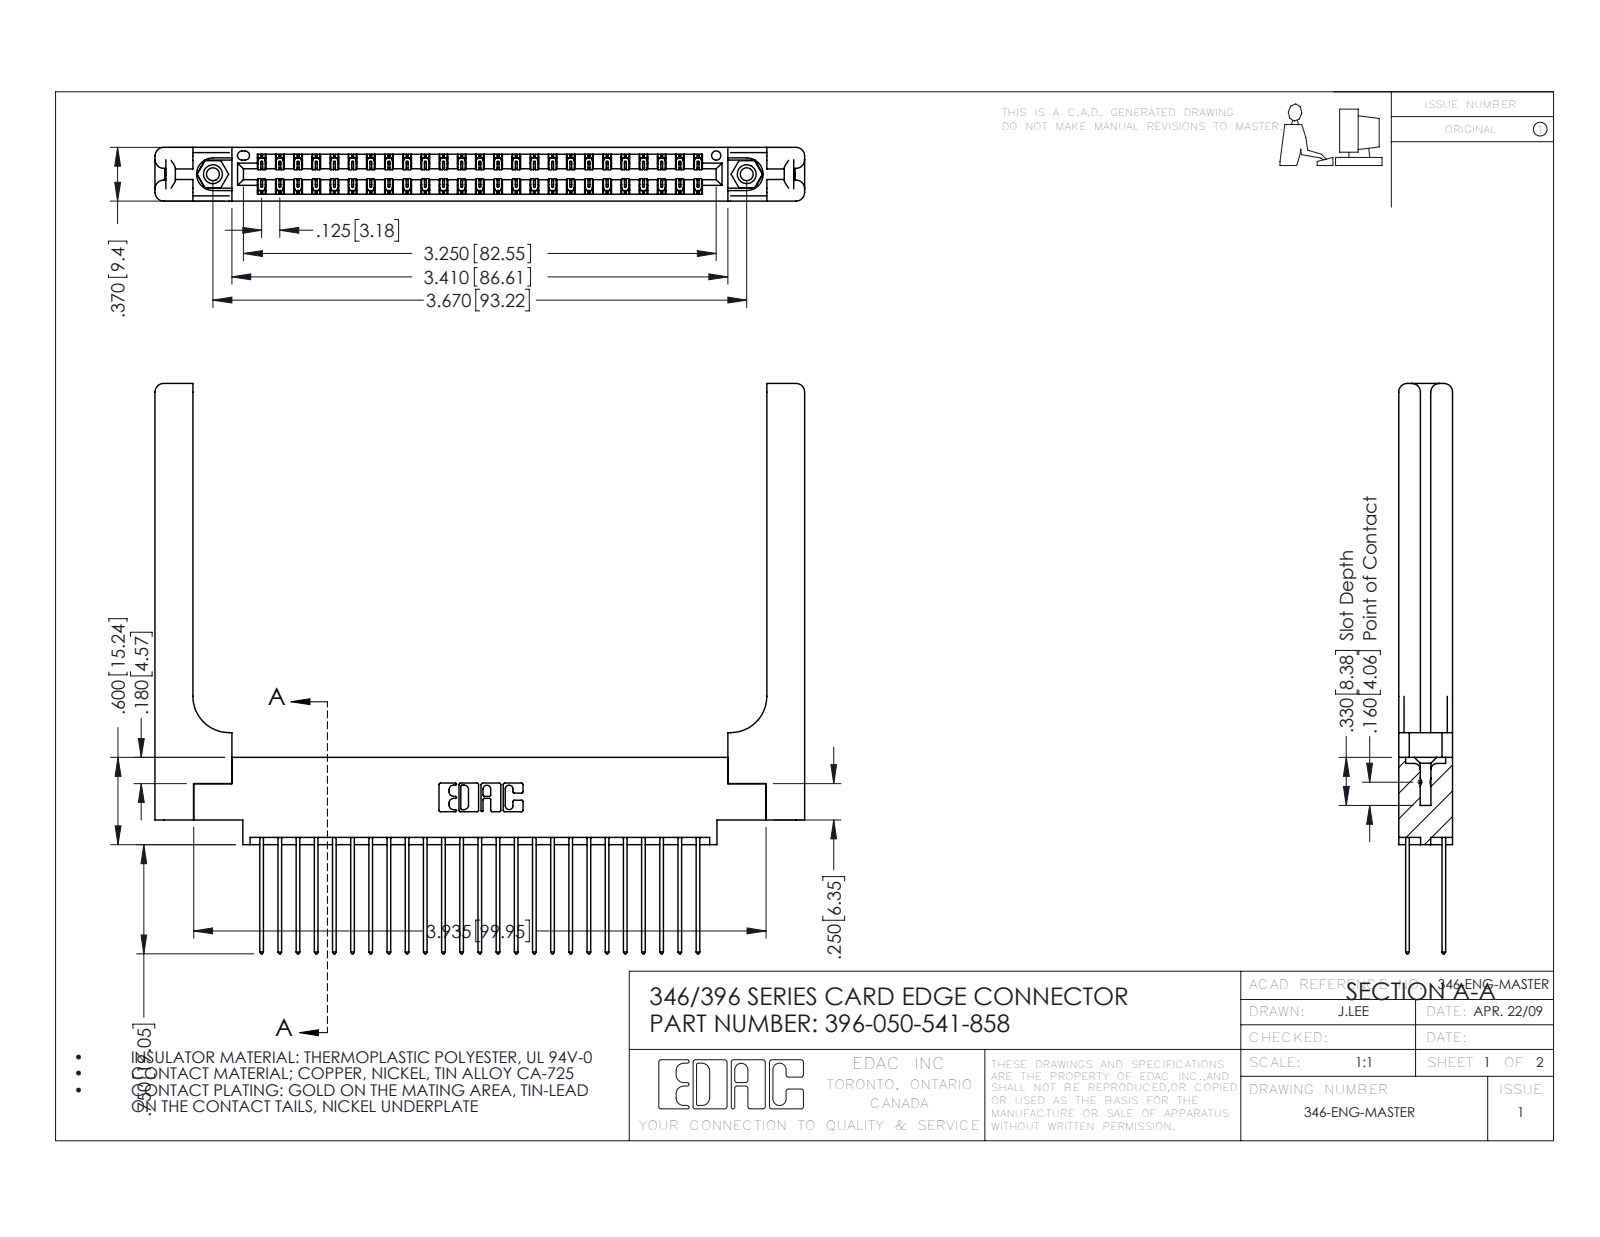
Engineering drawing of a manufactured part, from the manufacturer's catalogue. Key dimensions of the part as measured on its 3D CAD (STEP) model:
Part name (STEP PRODUCT): 346 Part_0.170 Offset - 0.156 Dia-TH; 346-220-058_345-220-058; 396-050-541-858; 345-250-001_345-250-001-102 (+1 more)
STEP written by: SolidWorks 2016 (CONFIG_CONTROL_DESIGN)
Units: inches
Bodies: 55 solids, 2982 faces (1978 planar, 944 cylindrical, 60 other)
Overall size (bounding box): 4.466 × 3.92 × 0.37
Volume: 1.132 in³ · Surface area: 33.27 in²
Round holes (diameter × count): ⌀0.089 ×2, ⌀0.125 ×2, ⌀0.156 ×2, ⌀0.064 ×1
Round bosses / shafts (diameter × count): ⌀0.155 ×2
Partial cylindrical surfaces — rounded edges, fillets, slot ends (radius × count): R0.006 ×75, R0.01 ×50, R0.01 ×22, R0.06 ×16, R0.007 ×6, R0.031 ×6, R0.026 ×3, R0.014 ×2
Main face-to-face distances: 0.37, 0.072, 0.048, 0.322, 0.25, 0.025, 0.298, 0.148, 0.15, 0.275
Hole centre spacings: 0.246, 3.462, 3.67
